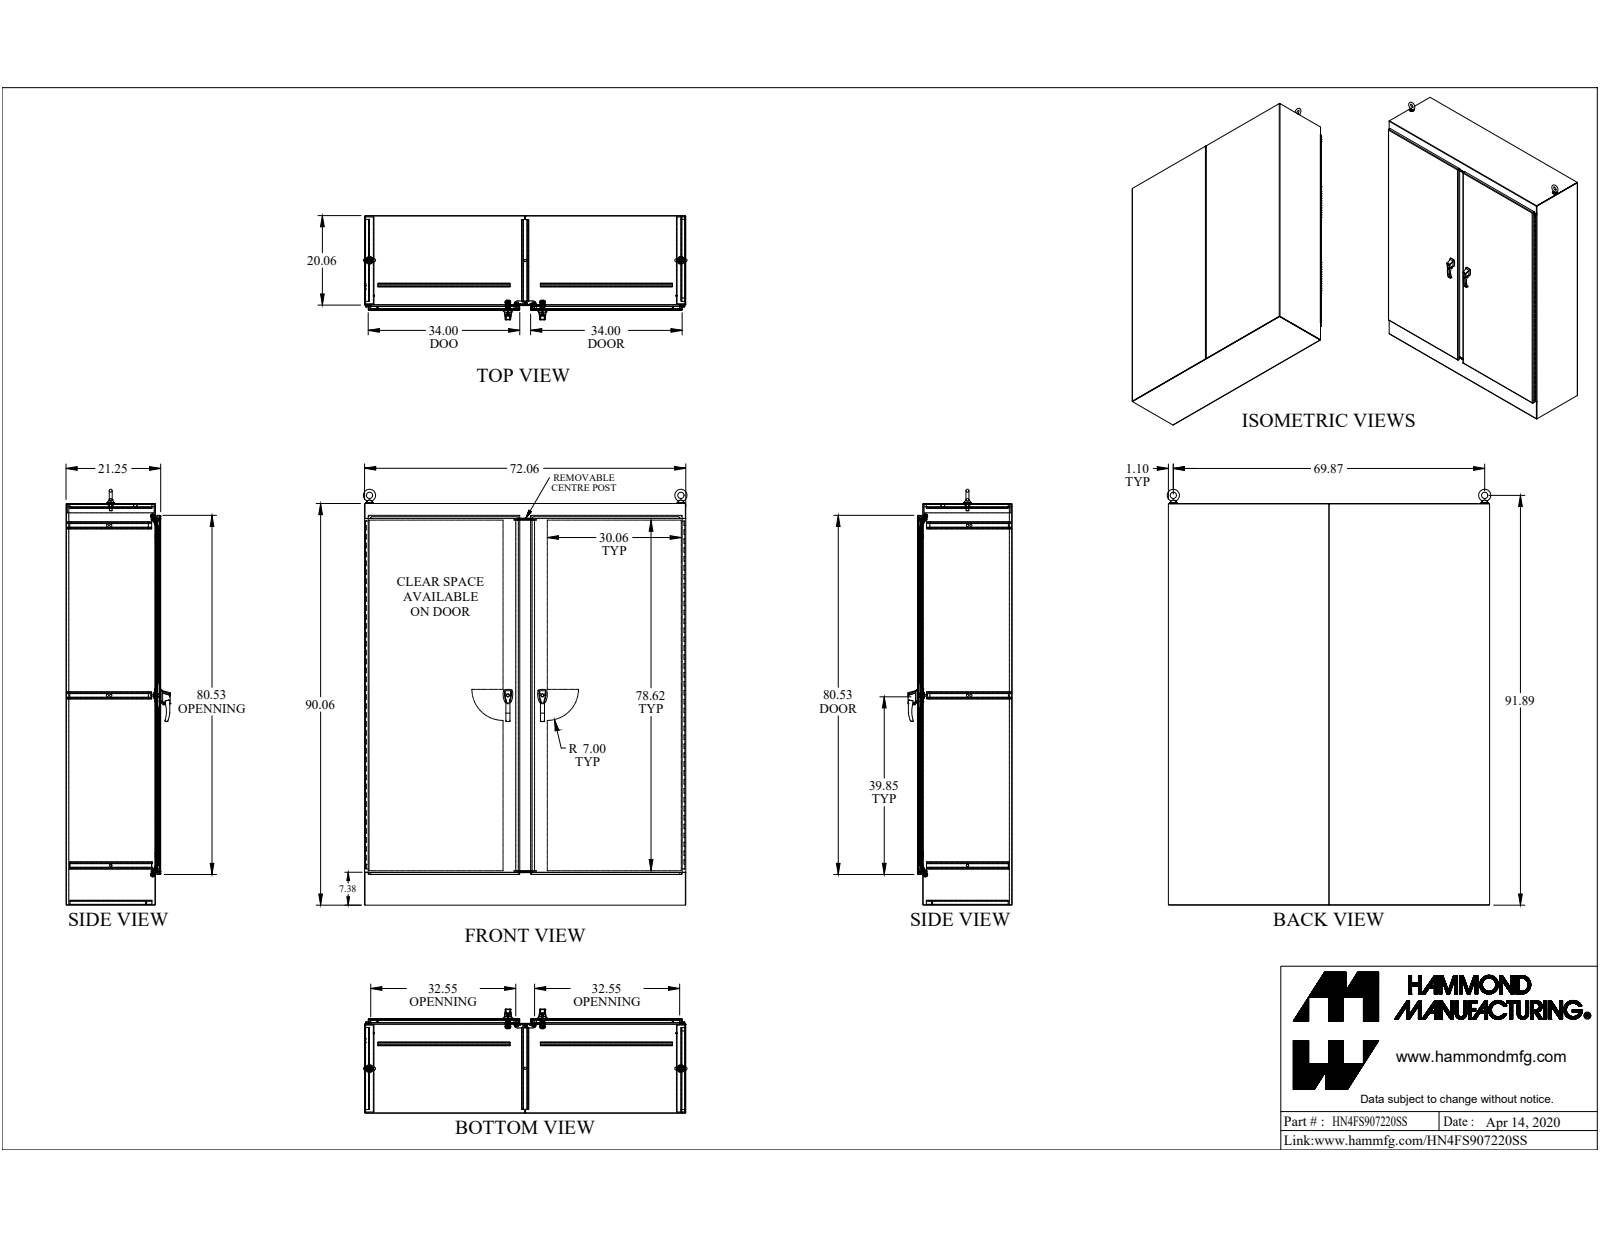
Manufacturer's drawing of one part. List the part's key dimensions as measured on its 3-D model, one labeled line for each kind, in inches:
Part name (STEP PRODUCT): HN4FS907220SS
STEP written by: SolidWorks 2019 (CONFIG_CONTROL_DESIGN)
Units: inches
Bodies: 106 solids, 3187 faces (1671 planar, 1270 cylindrical, 246 other)
Overall size (bounding box): 93.256 × 72.604 × 23.362
Volume: 2 193 in³ · Surface area: 46 373 in²
Round holes (diameter × count): ⌀0.304 ×26, ⌀0.35 ×8, ⌀0.25 ×7, ⌀0.5 ×7, ⌀0.257 ×4, ⌀0.28 ×4, ⌀0.281 ×4, ⌀0.313 ×4, ⌀0.39 ×4, ⌀0.413 ×4, ⌀0.201 ×3, ⌀0.313 ×3
Round bosses / shafts (diameter × count): ⌀1 ×4, ⌀0.75 ×4, ⌀0.63 ×4, ⌀0.625 ×4, ⌀0.44 ×4, ⌀0.37 ×4, ⌀0.313 ×4, ⌀0.25 ×4
Partial cylindrical surfaces — rounded edges, fillets, slot ends (radius × count): R0.043 ×54, R0.138 ×48, R0.5 ×33, R0.018 ×32, R0.1 ×28, R0.125 ×27, R0.06 ×24, R0.036 ×16
Main face-to-face distances: 0.095, 21.152, 21.057, 21.247, 71.965, 89.965, 1.187, 19.965, 71.87, 72.06
Hole centre spacings: 6, 70.584, 12, 71.345, 18, 72.595, 24, 74.311
